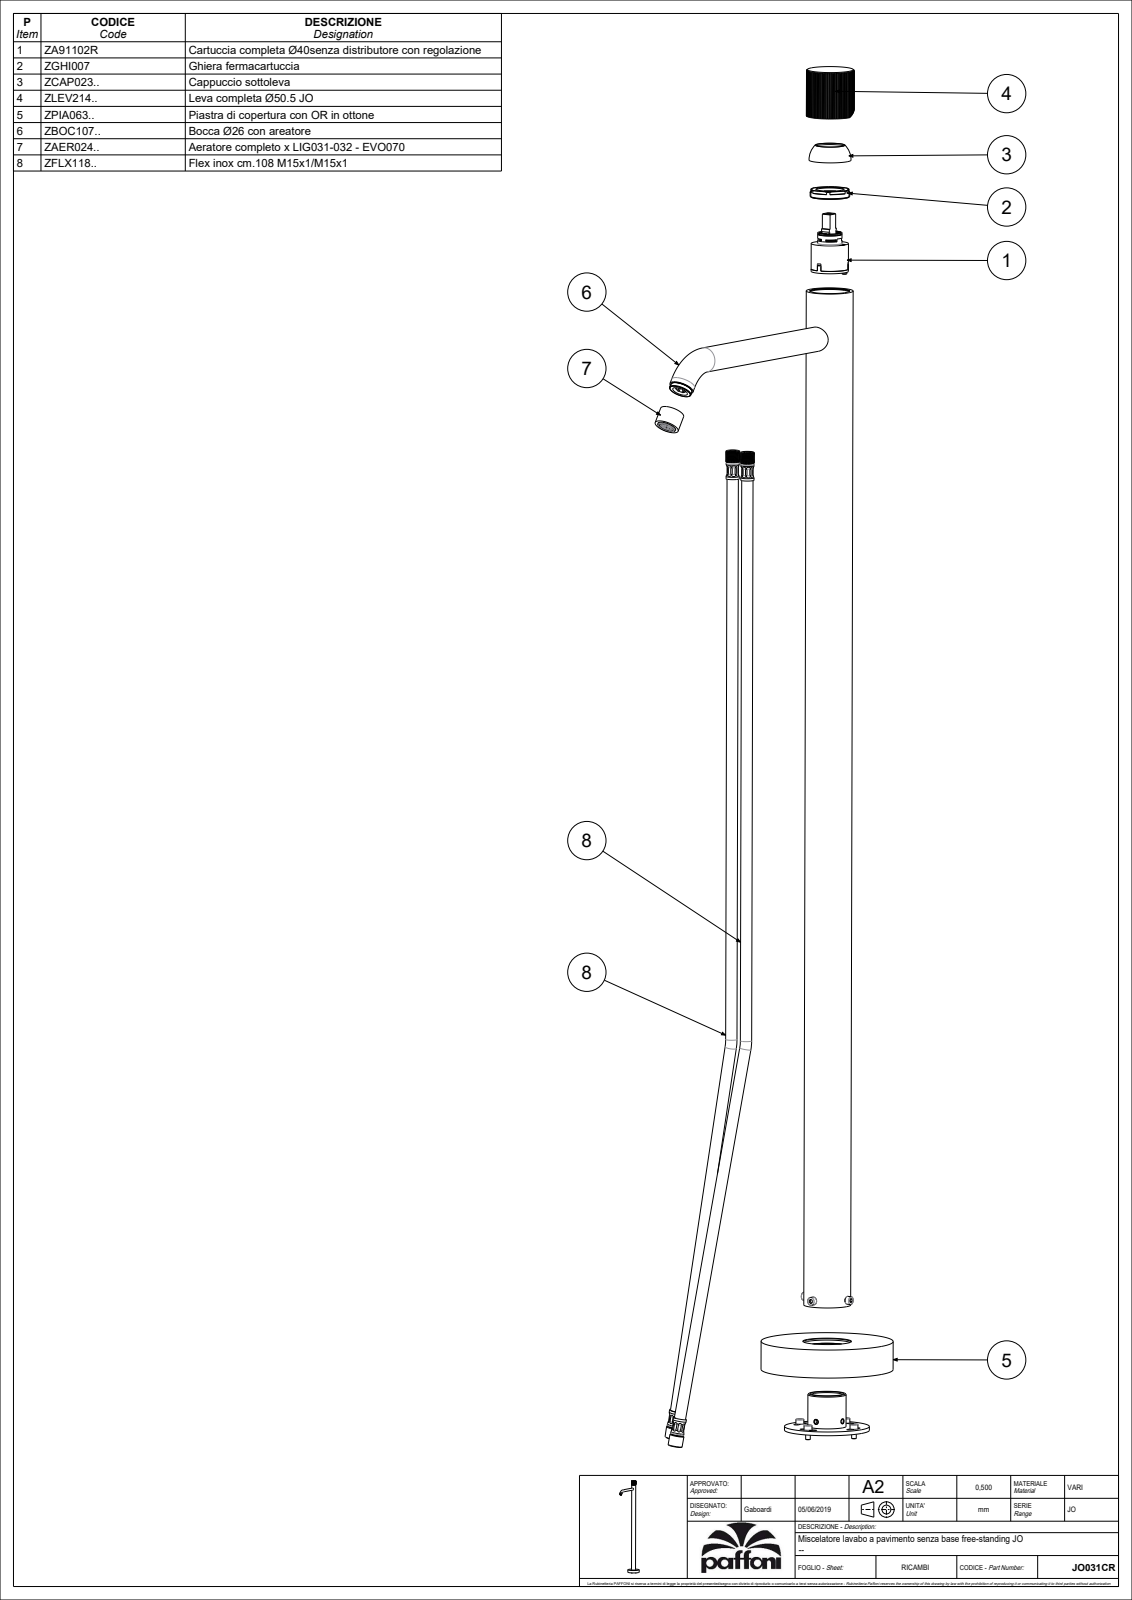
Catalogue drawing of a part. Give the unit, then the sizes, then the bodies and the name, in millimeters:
Units: millimetres
Overall size (bounding box): 1141.3 × 364.39 × 140
Round holes (diameter × count): ⌀3 ×1, ⌀4.5 ×1, ⌀5.5 ×1, ⌀8 ×1, ⌀47 ×1
Round bosses / shafts (diameter × count): ⌀26 ×2, ⌀140 ×1, ⌀49.7 ×1, ⌀19 ×1, ⌀18.8 ×1, ⌀7.6 ×1
Partial cylindrical surfaces — rounded edges, fillets, slot ends (radius × count): R25.25 ×1
Main face-to-face distances: 30, 1138.3, 1108.3, 35.01, 35, 1105, 1075, 33.3, 35.02, 1089
Hole centre spacings: 76.73
Volume: 2 709 000 mm³ · Surface area: 253 748 mm²
Bodies: 1 solid, 267 faces (158 planar, 94 cylindrical, 15 other)
Part name (STEP PRODUCT): JO031CR
STEP written by: CREO PARAMETRIC BY PTC INC, 2020044 (CONFIG_CONTROL_DESIGN)
